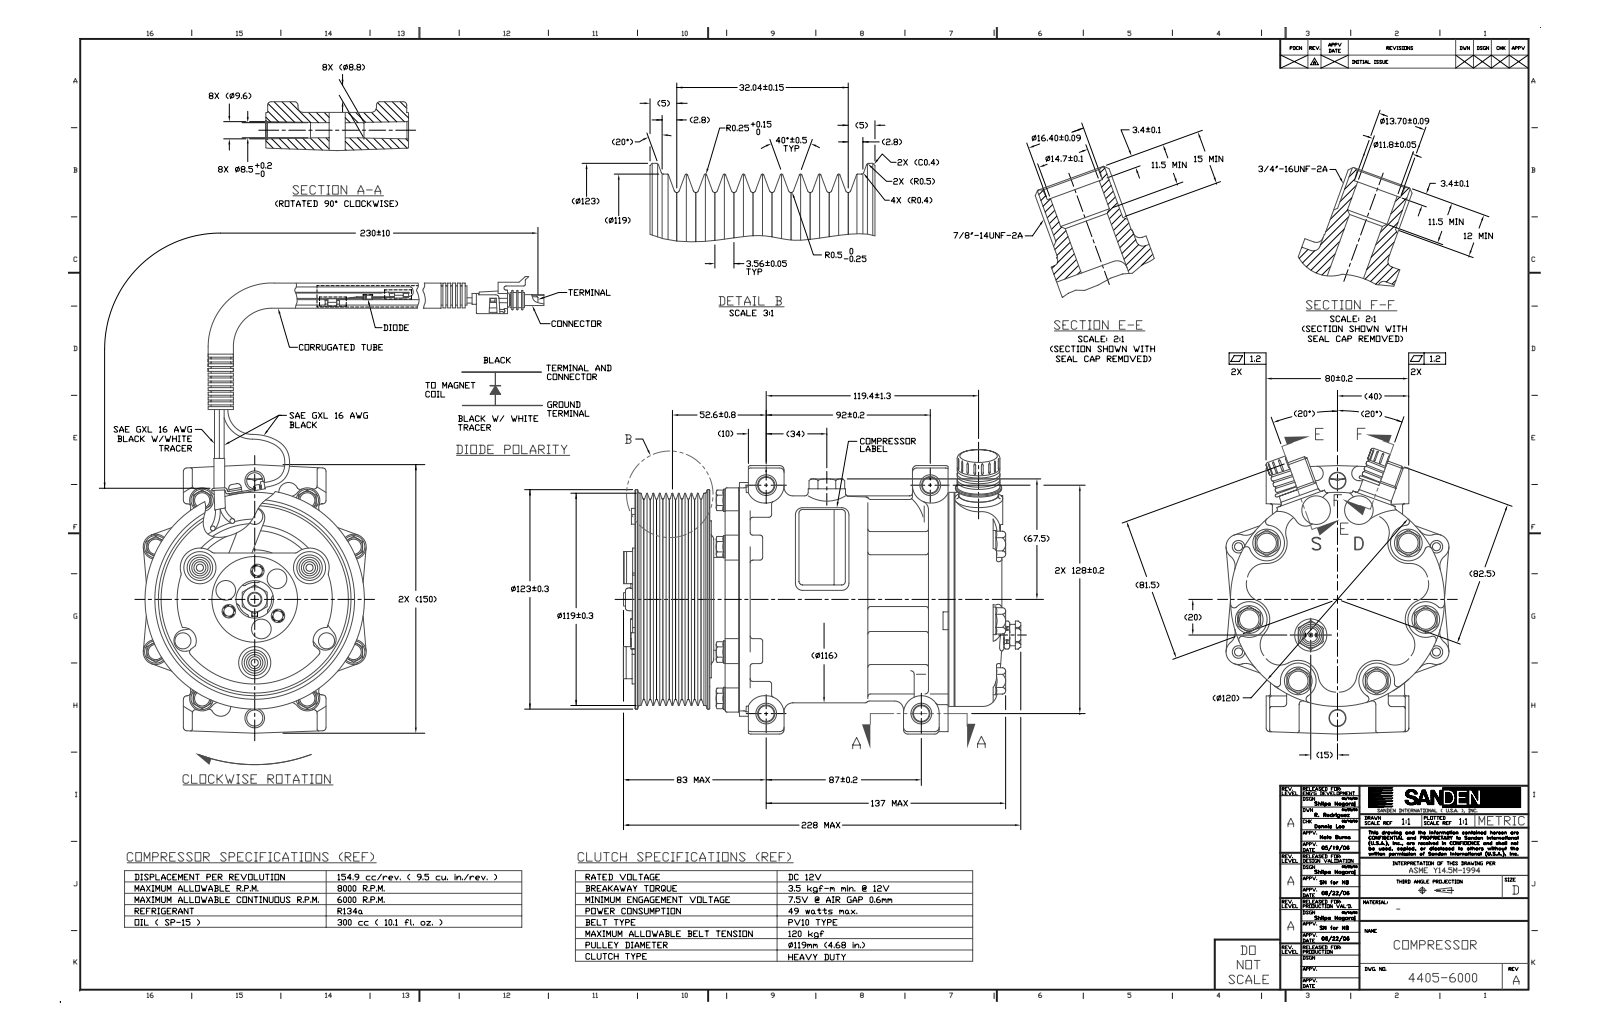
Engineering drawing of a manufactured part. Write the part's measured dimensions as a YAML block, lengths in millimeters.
part_name: "SANDEN_4405_REV_B_COMPR_AC"
step_written_by: "SolidWorks 2007 (CONFIG_CONTROL_DESIGN)"
units: millimeters
bodies: {solids: 1, faces: 2492, planar: 620, cylindrical: 650, other: 1222}
overall_size: [371.31, 224.3, 125]
volume: 2217000
surface_area: 264525
round_holes:
  - {diameter: 8.5, count: 12}
  - {diameter: 8, count: 6}
  - {diameter: 11.9, count: 6}
  - {diameter: 5.1, count: 3}
  - {diameter: 6.35, count: 3}
  - {diameter: 7.5, count: 3}
  - {diameter: 9, count: 2}
  - {diameter: 3.5, count: 1}
  - {diameter: 4, count: 1}
  - {diameter: 11.8, count: 1}
  - {diameter: 12.9, count: 1}
  - {diameter: 13, count: 1}
round_bosses_or_shafts:
  - {diameter: 12.9, count: 8}
  - {diameter: 15.3, count: 6}
  - {diameter: 16, count: 5}
  - {diameter: 2.7, count: 5}
  - {diameter: 18, count: 3}
  - {diameter: 11, count: 3}
  - {diameter: 9, count: 3}
  - {diameter: 5, count: 3}
partial_cylinders:
  - {radius: 0.5, count: 43}
  - {radius: 2, count: 39}
  - {radius: 7, count: 32}
  - {radius: 1.5, count: 30}
  - {radius: 3, count: 24}
  - {radius: 2.5, count: 18}
  - {radius: 5, count: 17}
  - {radius: 10, count: 14}
face_to_face_distances: [45.02, 2, 44.92, 49.82, 4.8, 45.62, 0.6, 4.2, 6.4, 38.62]
hole_center_spacings: [62.85, 88.89, 42.09, 16, 31.48, 36.77, 59, 66.7]
